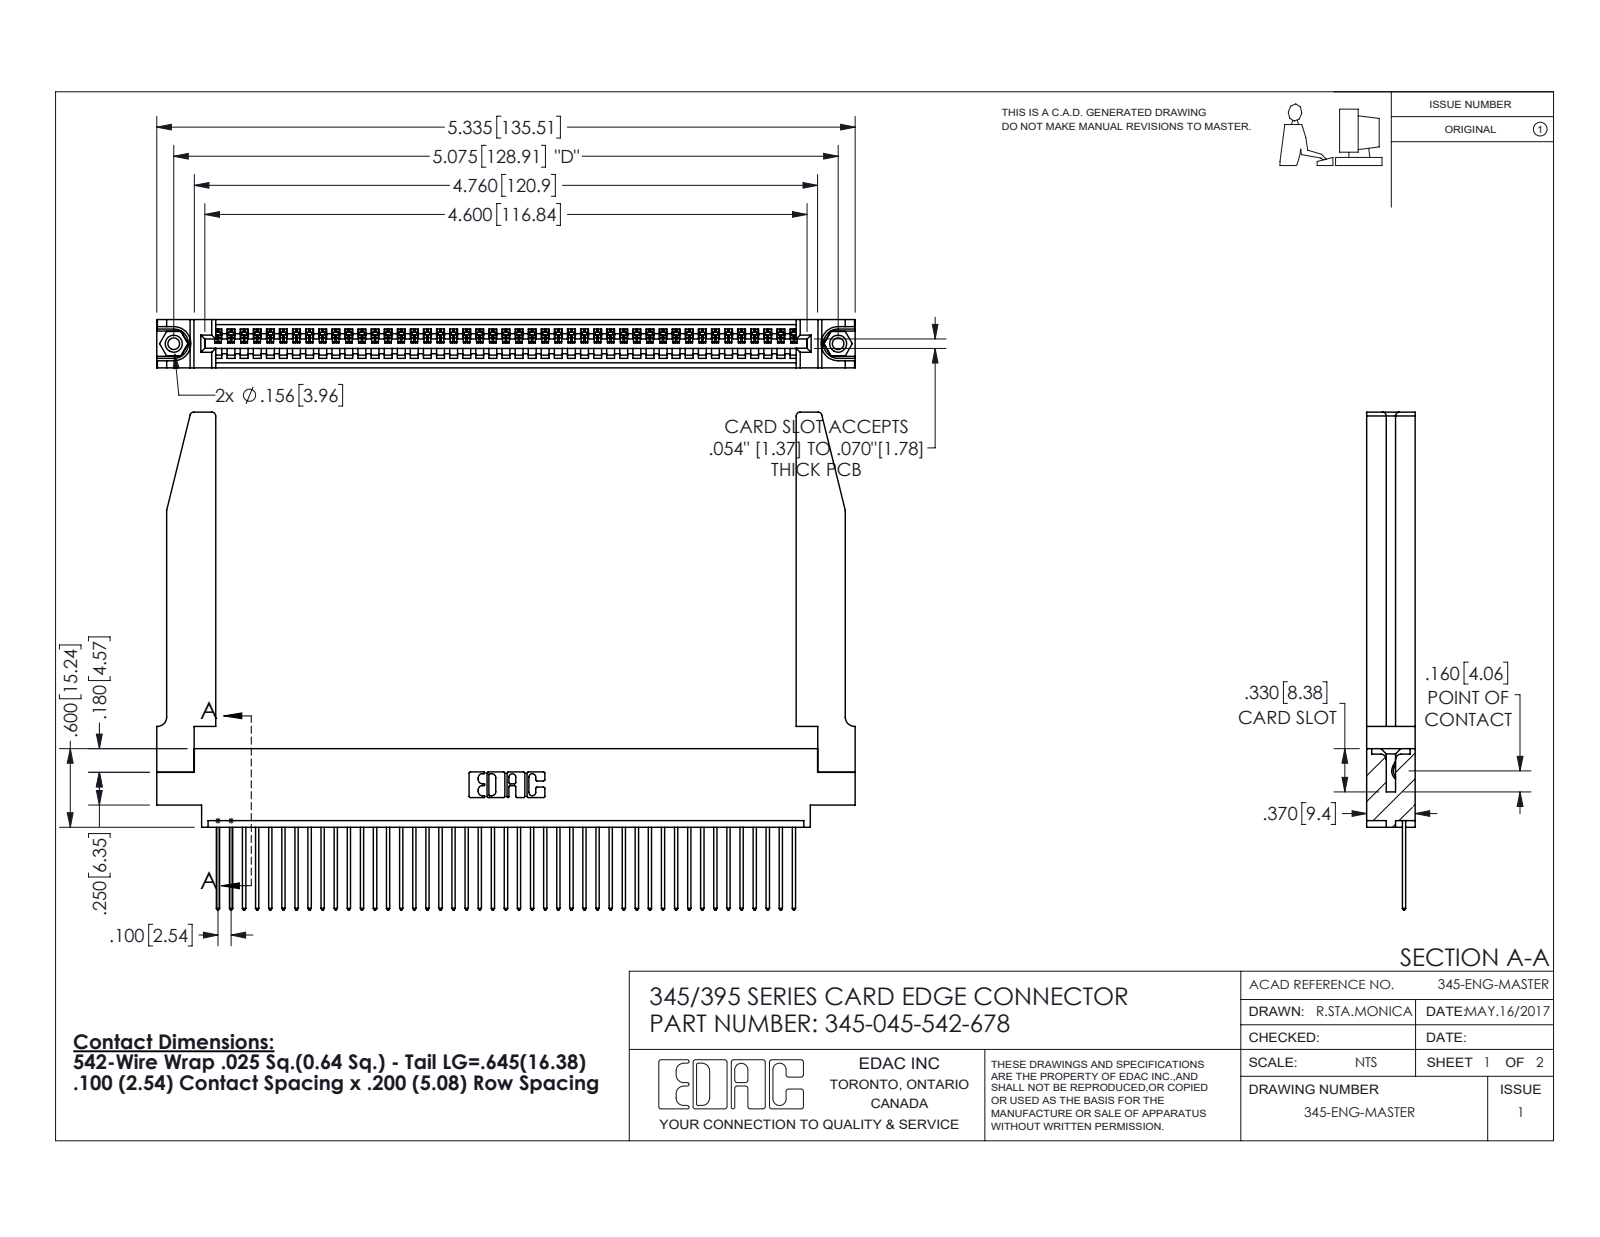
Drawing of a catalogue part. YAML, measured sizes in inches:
part_name: "345 Part_0.170 Offset - 0.156 Dia-TH; 345-045-542-678; 345-220-078_345-220-078; 345-250-001_345-250-001-102 (+1 more)"
step_written_by: "SolidWorks 2016 (CONFIG_CONTROL_DESIGN)"
units: inches
bodies: {solids: 50, faces: 2974, planar: 2026, cylindrical: 896, other: 52}
overall_size: [5.336, 3.802, 0.37]
volume: 1.26
surface_area: 38.39
round_holes:
  - {diameter: 0.089, count: 2}
  - {diameter: 0.125, count: 2}
  - {diameter: 0.156, count: 2}
  - {diameter: 0.064, count: 1}
round_bosses_or_shafts:
  - {diameter: 0.155, count: 2}
partial_cylinders:
  - {radius: 0.006, count: 90}
  - {radius: 0.01, count: 90}
  - {radius: 0.01, count: 22}
  - {radius: 0.03, count: 8}
  - {radius: 0.007, count: 6}
  - {radius: 0.031, count: 6}
  - {radius: 0.026, count: 3}
  - {radius: 0.031, count: 2}
face_to_face_distances: [0.37, 0.072, 0.298, 0.098, 0.272, 0.025, 0.2, 0.225, 0.148, 0.15]
hole_center_spacings: [0.27, 4.839, 5.075]
